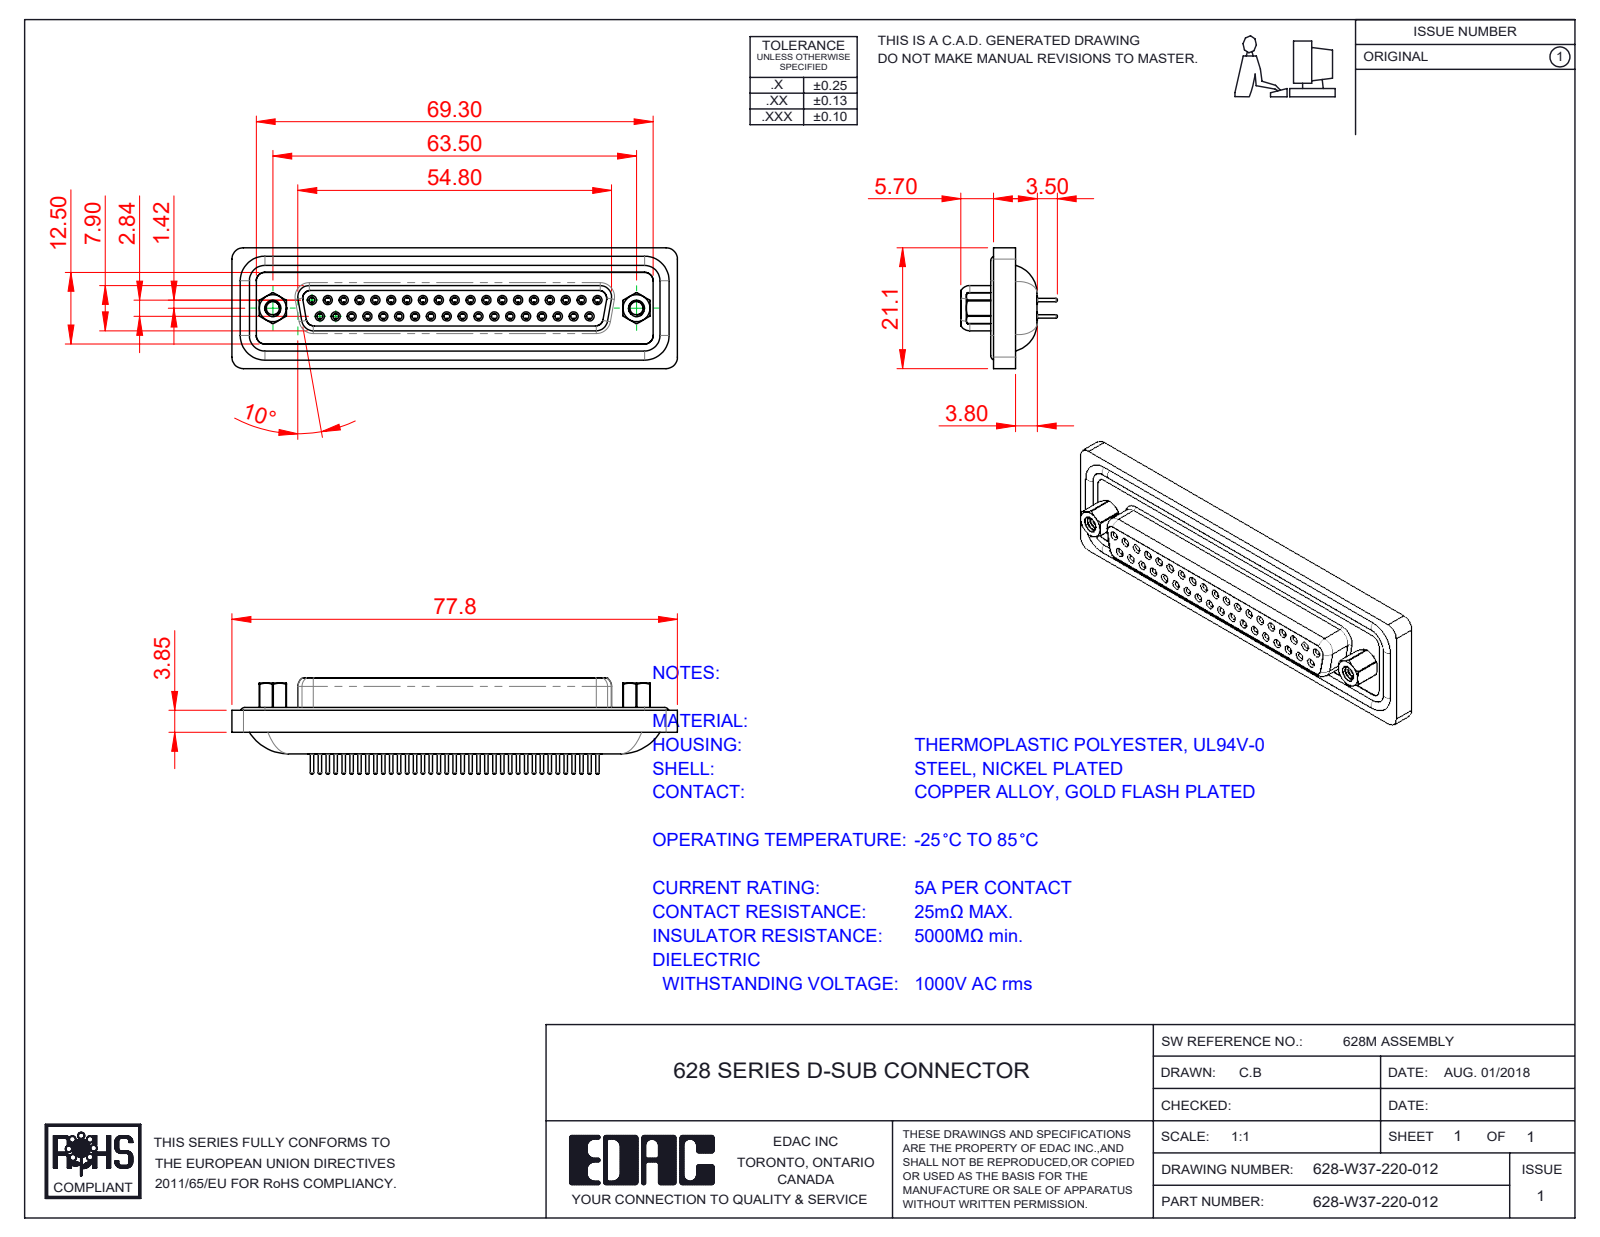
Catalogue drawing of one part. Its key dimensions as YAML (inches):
part_name: "628-W37-220-012; 628W Waterproof Housing_37 Contacts; 628W Housing_37 Contacts; 628W 4-40 Hex Standoff (+4 more)"
step_written_by: "SolidWorks 2020 (CONFIG_CONTROL_DESIGN)"
units: inches
bodies: {solids: 45, faces: 2532, planar: 656, cylindrical: 997, other: 879}
overall_size: [3.063, 0.831, 0.663]
volume: 0.674
surface_area: 27.55
round_holes:
  - {diameter: 0.039, count: 37}
  - {diameter: 0.043, count: 37}
  - {diameter: 0.059, count: 37}
  - {diameter: 0.067, count: 37}
  - {diameter: 0.071, count: 37}
  - {diameter: 0.079, count: 37}
  - {diameter: 0.089, count: 2}
  - {diameter: 0.09, count: 2}
  - {diameter: 0.157, count: 2}
  - {diameter: 0.189, count: 2}
  - {diameter: 0.197, count: 2}
round_bosses_or_shafts:
  - {diameter: 0.063, count: 41}
  - {diameter: 0.087, count: 37}
  - {diameter: 0.024, count: 37}
  - {diameter: 0.059, count: 8}
  - {diameter: 0.193, count: 2}
  - {diameter: 0.11, count: 2}
partial_cylinders:
  - {radius: 0.079, count: 16}
  - {radius: 0.059, count: 14}
  - {radius: 0.053, count: 8}
  - {radius: 0.106, count: 6}
  - {radius: 0.02, count: 4}
  - {radius: 0.035, count: 4}
  - {radius: 0.063, count: 4}
  - {radius: 0.069, count: 4}
face_to_face_distances: [0.016, 0.293, 0.295, 0.333, 0.244, 0.537, 0.148, 0.161, 0.043, 0.108]
hole_center_spacings: [0.124, 0.109, 0.218, 0.327, 0.198, 0.295, 0.436, 0.545]
